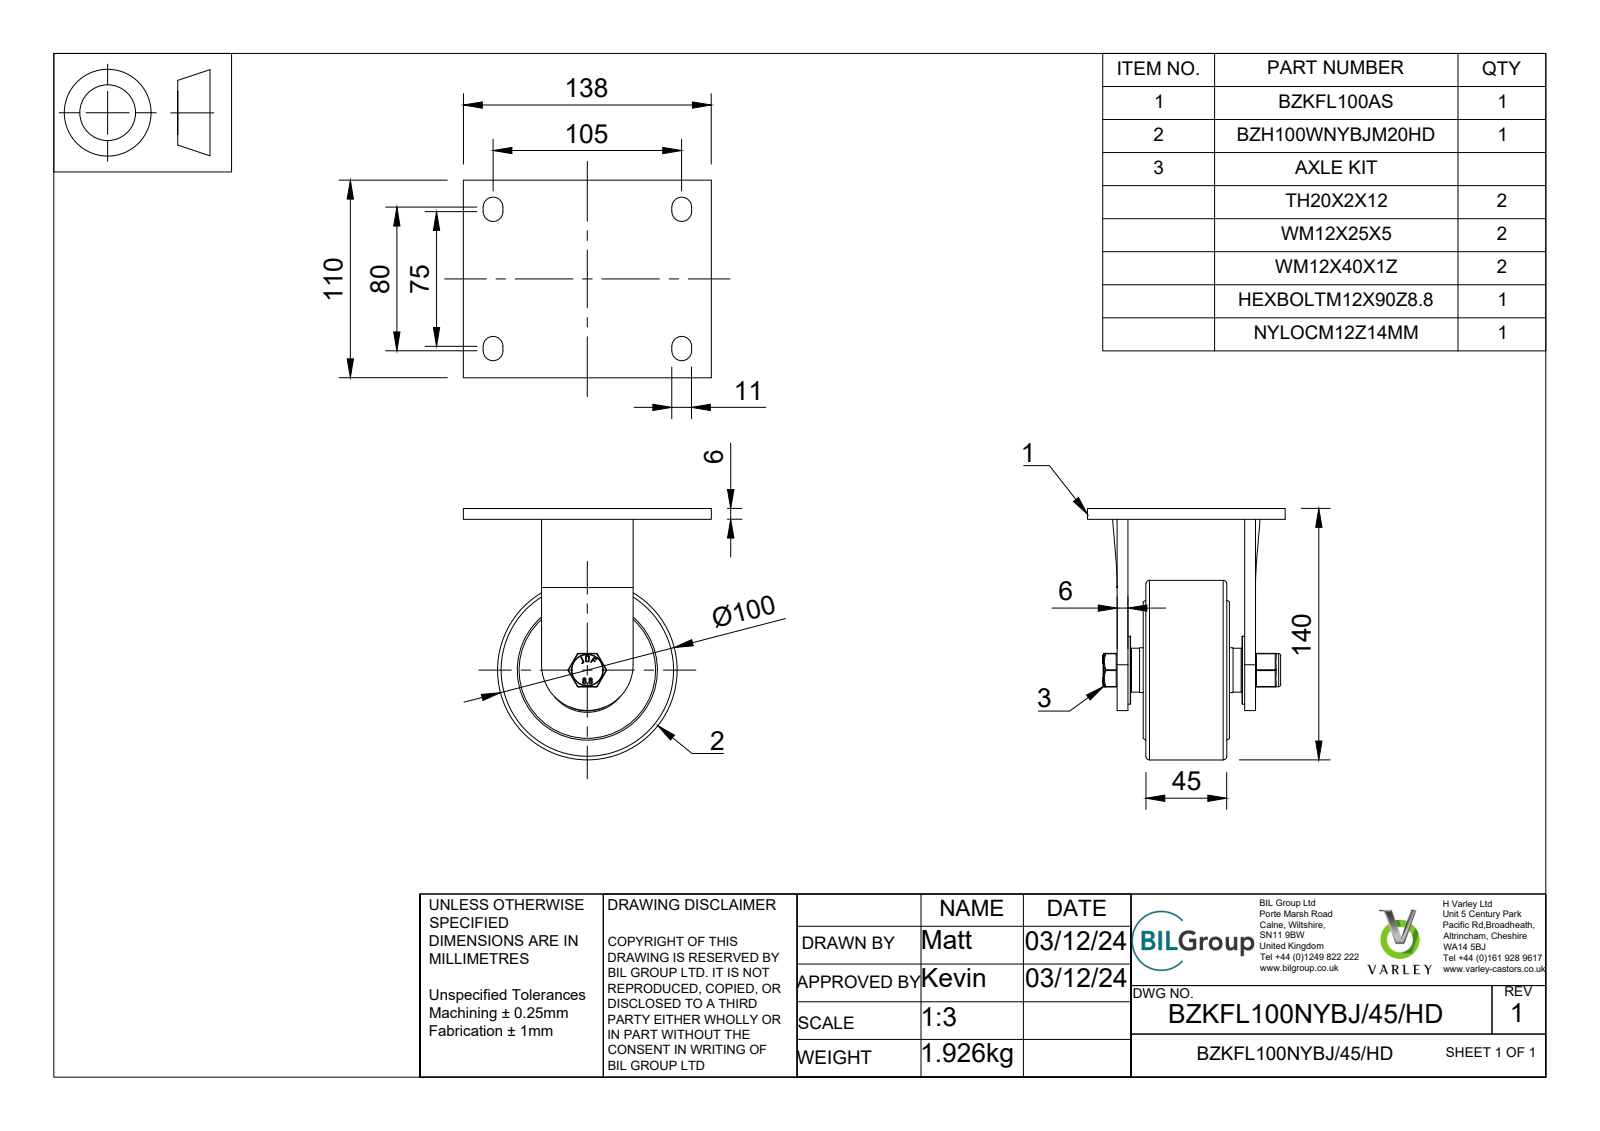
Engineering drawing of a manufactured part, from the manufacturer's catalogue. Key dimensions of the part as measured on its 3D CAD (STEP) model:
Part name (STEP PRODUCT): BZKFL100NYBJ/45/HD v3; BZKFL100AS v1; BZKFL100AS; FABRICATED STEEL BRACKET (+7 more)
STEP written by: Autodesk Translation Framework v13.20.0.188 (AP242_MANAGED_MODEL_BASED_3D_ENGINEERING_MIM_LF)
Units: millimetres
Bodies: 38 solids, 562 faces (232 planar, 191 cylindrical, 139 other)
Overall size (bounding box): 140 × 138 × 110
Volume: 497 535 mm³ · Surface area: 144 858 mm²
Round holes (diameter × count): ⌀12 ×1, ⌀12.2 ×1, ⌀12.75 ×1, ⌀13 ×1, ⌀13.2 ×1, ⌀14 ×1, ⌀20 ×1, ⌀28.5 ×1, ⌀29.5 ×1, ⌀40.5 ×1, ⌀42 ×1, ⌀47 ×1
Round bosses / shafts (diameter × count): ⌀100 ×1, ⌀41.5 ×1, ⌀37.75 ×1, ⌀30.5 ×1, ⌀27 ×1, ⌀25 ×1, ⌀24.5 ×1, ⌀24 ×1
Partial cylindrical surfaces — rounded edges, fillets, slot ends (radius × count): R0.5 ×20, R5.5 ×8, R0.47 ×4, R0.9 ×4, R0.89 ×2, R0.89 ×2, R6.78 ×2, R7.47 ×2
Main face-to-face distances: 6, 8.5, 1.5, 55, 56.5, 16, 14.5, 62.5, 71, 65
